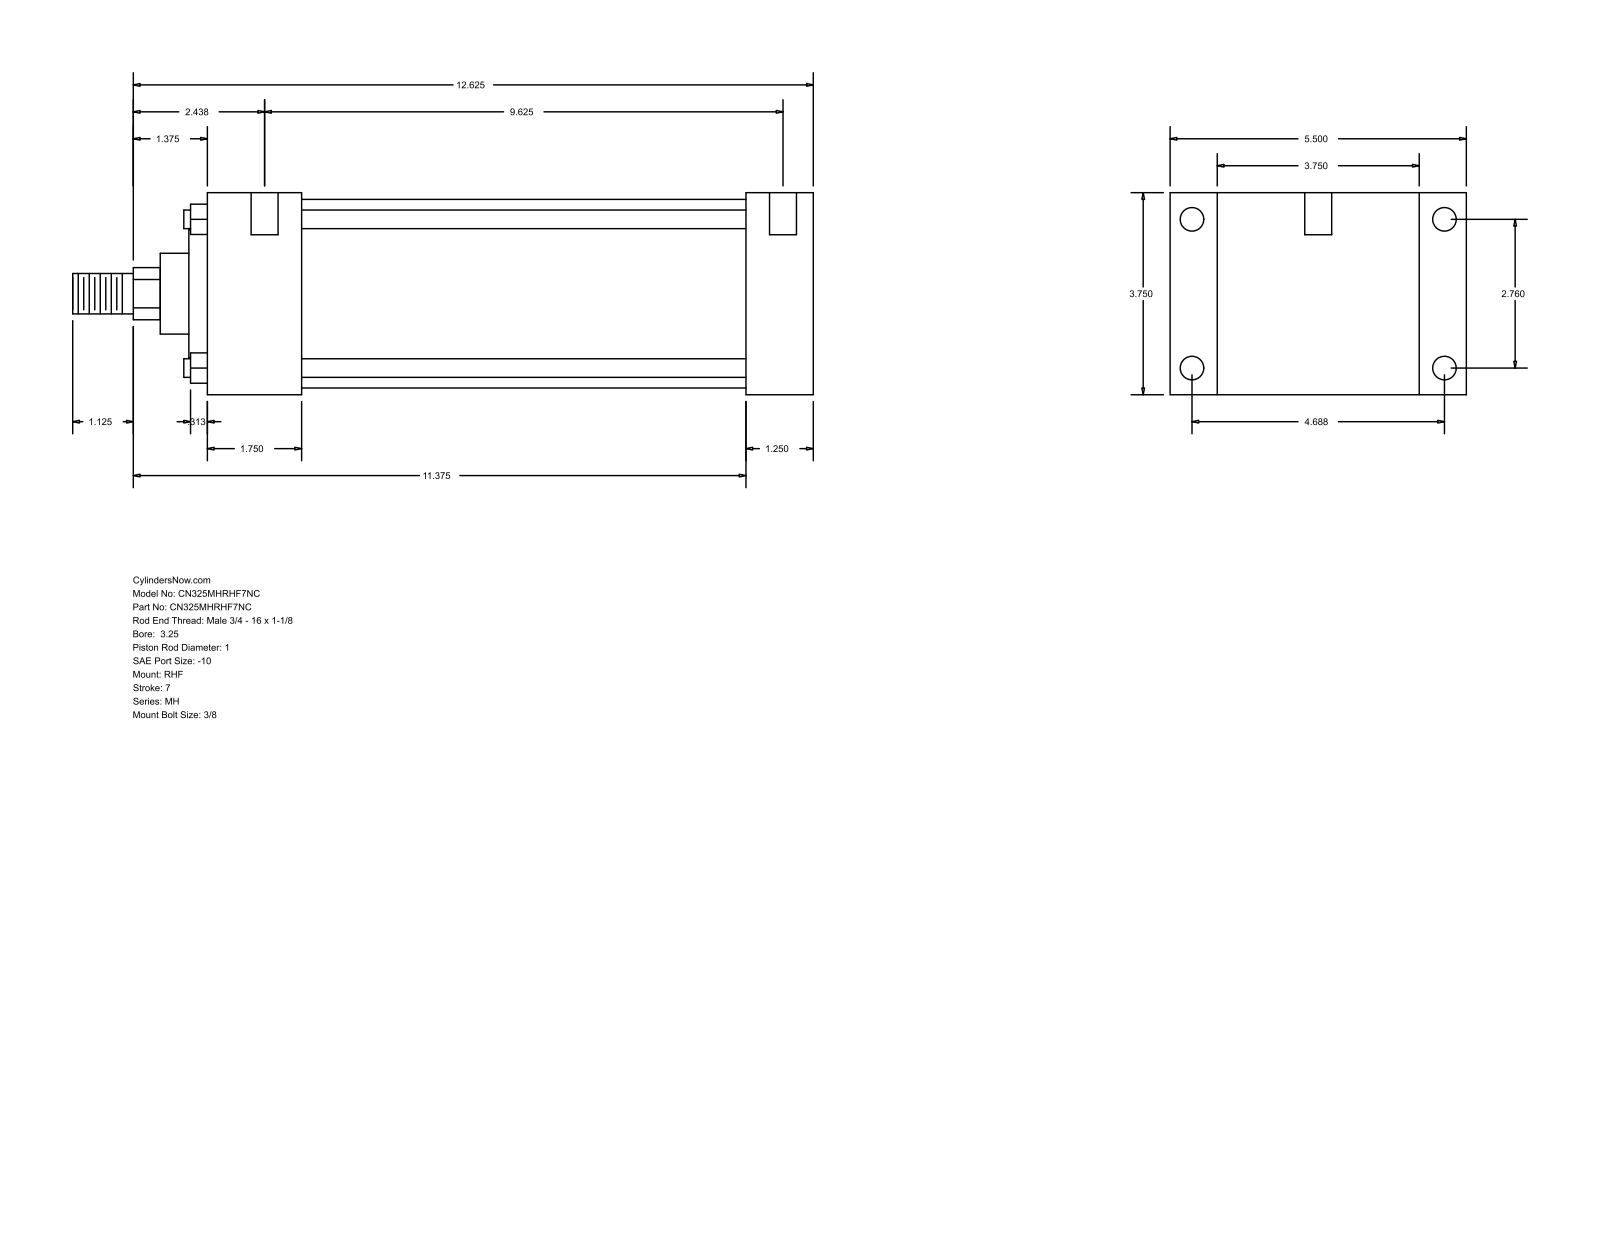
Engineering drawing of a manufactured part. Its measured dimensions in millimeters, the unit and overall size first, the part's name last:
Units: millimetres
Overall size (bounding box): 349.25 × 139.7 × 95.25
Round holes (diameter × count): ⌀5.56 ×4, ⌀11.13 ×4, ⌀12.7 ×2
Round bosses / shafts (diameter × count): ⌀8.76 ×4, ⌀88.9 ×1, ⌀60.33 ×1, ⌀38.1 ×1, ⌀25.4 ×1, ⌀19.05 ×1
Partial cylindrical surfaces — rounded edges, fillets, slot ends (radius × count): R12.29 ×1
Main face-to-face distances: 95.24, 31.75, 22.23, 117.47, 254.01, 285.76, 139.7, 44.46, 209.55, 241.3
Hole centre spacings: 70.1, 119.06, 138.16, 250.82, 1.58, 4.76, 244.48, 246.06
Bodies: 0 solids, 90 faces (61 planar, 29 cylindrical, 0 other)
Part name (STEP PRODUCT): MH_RHF__0325_1
STEP written by: GSSL Pune (CONFIG_CONTROL_DESIGN)
